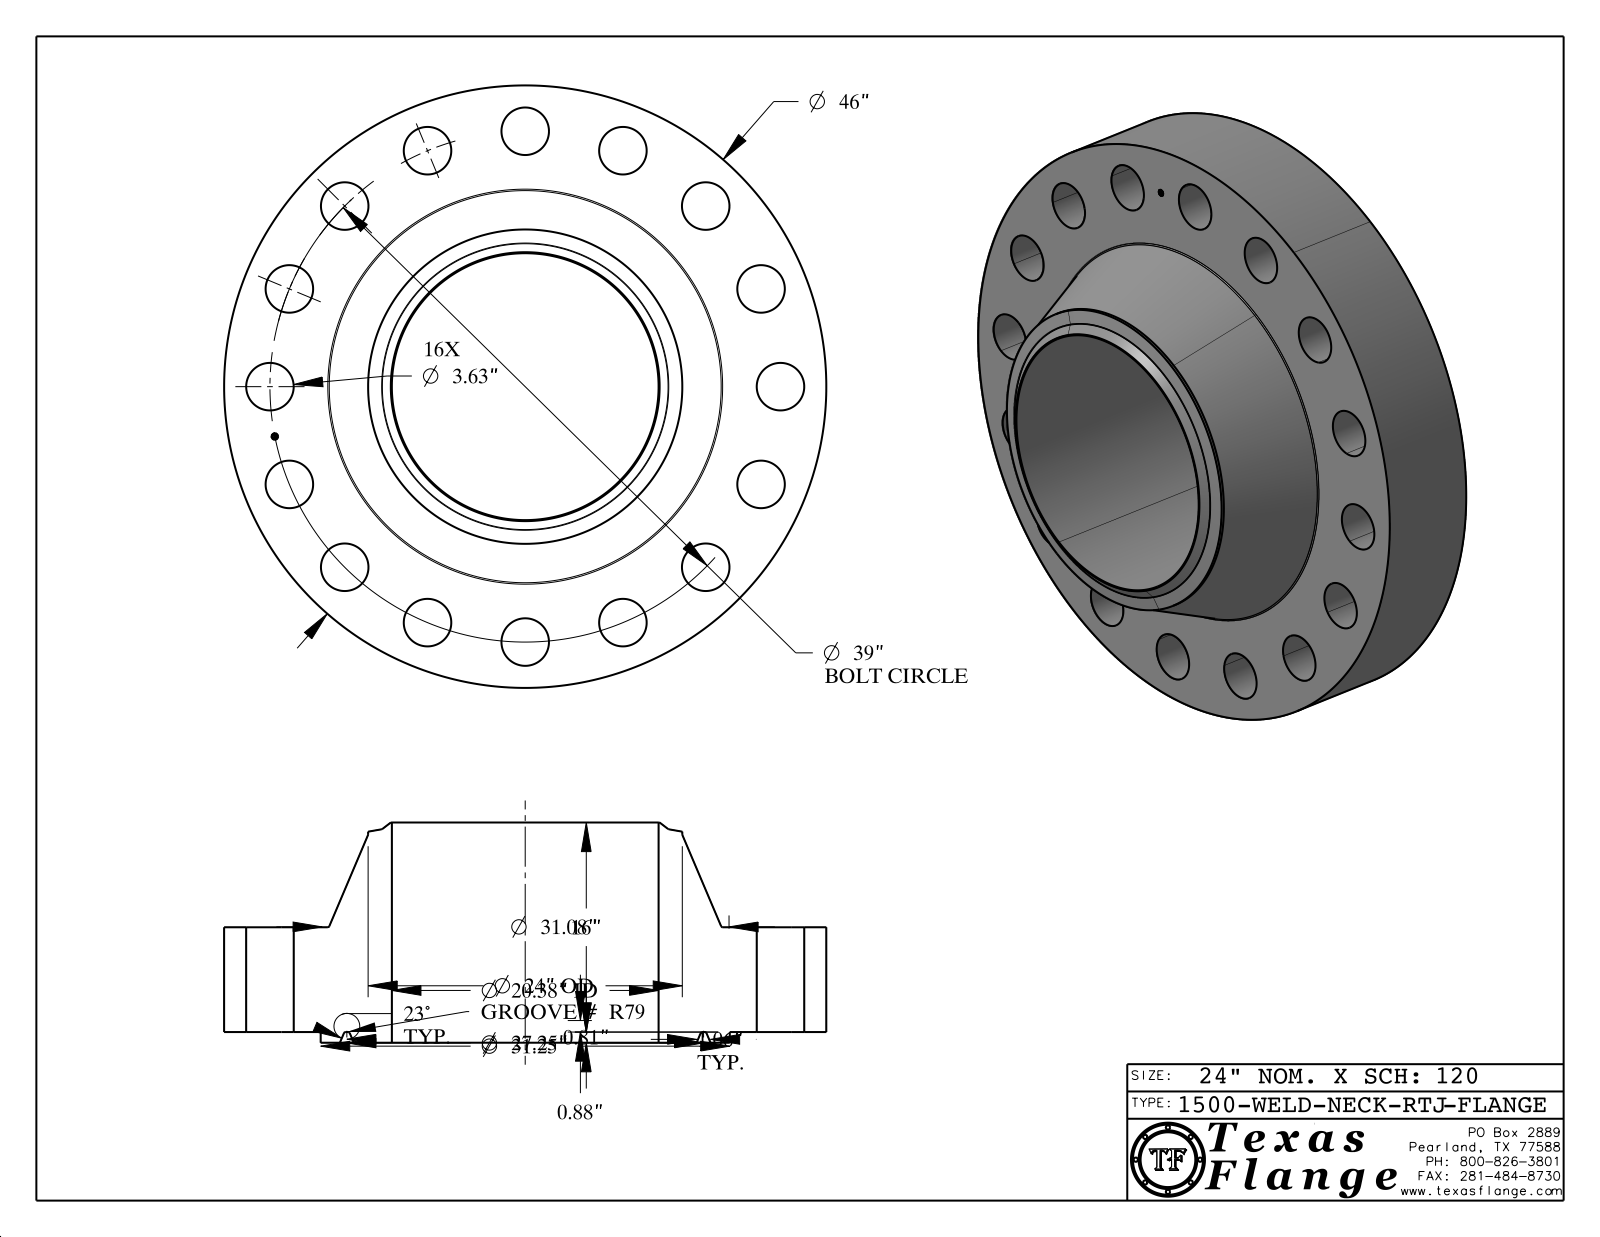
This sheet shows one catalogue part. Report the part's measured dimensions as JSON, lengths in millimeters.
{"part_name": "1500-WELD-NECK-RTJ", "step_written_by": "CATIA V5 STEP AP214 (AUTOMOTIVE_DESIGN)", "units": "millimeters", "bodies": {"solids": 1, "faces": 449, "planar": 371, "cylindrical": 60, "other": 18}, "overall_size": [1168.4, 1168.4, 427.1], "volume_mm3": 188300000, "surface_area_mm2": 4275000, "round_holes": [[92.2, 16], [12.6, 1], [517.6, 1]], "round_bosses_or_shafts": [[0.8, 8], [1168.4, 1], [793.8, 1], [609.6, 1], [9.9, 1]], "face_to_face_distances": [203.2, 20.7, 223.9, 427.1, 406.4, 223.5, 202.8, 0.4, 203.6, 3.8], "hole_center_spacings": [495.3, 550.3, 700.5, 971.6, 379.1, 915.2, 193.2, 193.3]}
